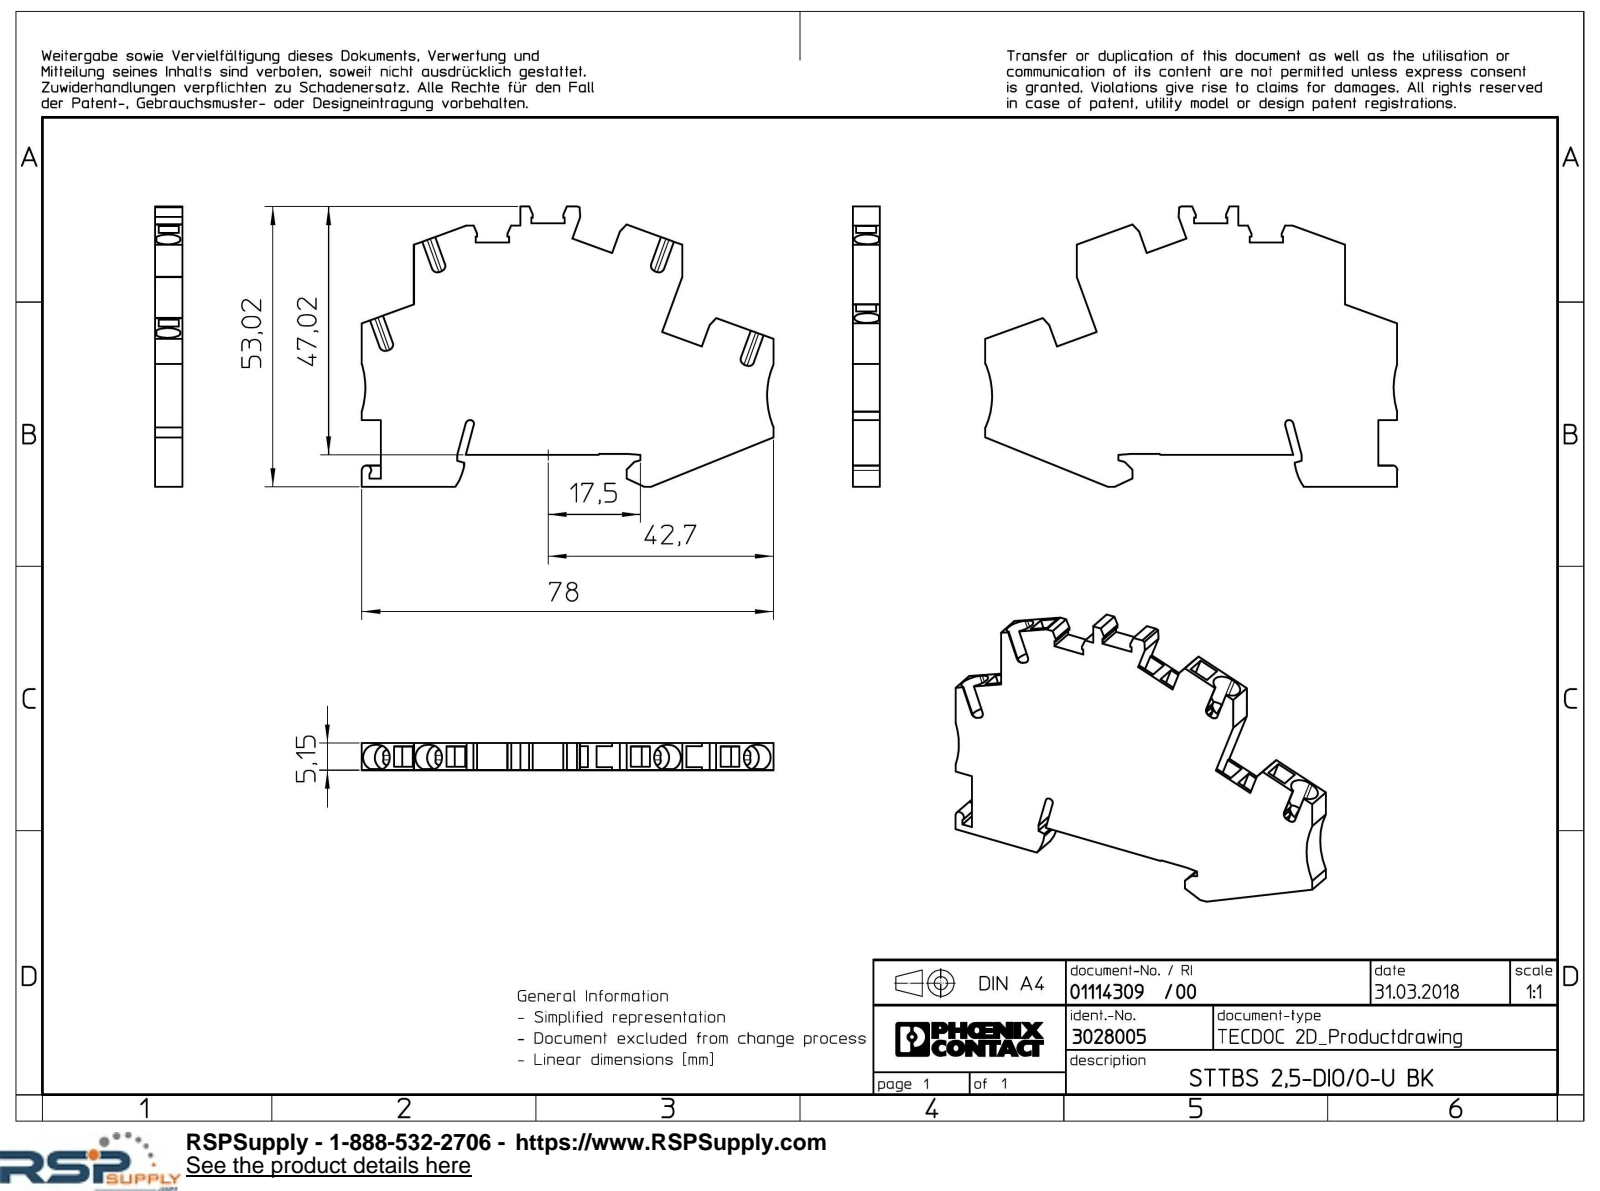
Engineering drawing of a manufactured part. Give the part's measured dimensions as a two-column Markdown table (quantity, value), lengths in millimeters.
| quantity | value |
| --- | --- |
| part name | STTBS2.5-DIO-O-U-BK-Select |
| STEP written by | Creo Elements/Direct Modeling 18.1I 14-Aug-2016 (C) Parametric Technology GmbH (AUTOMOTIVE_DESIGN) |
| units | millimeters |
| bodies | 1 solid, 199 faces (156 planar, 31 cylindrical, 12 other) |
| overall size | 78 × 53.02 × 5.15 |
| volume | 13 020 mm³ |
| surface area | 9 168 mm² |
| partial cylindrical surfaces (radius × count) | 1 × 16, 2.4 × 8, 15 × 2, 0.2 × 1, 0.7 × 1, 0.8 × 1, 0.9 × 1, 9.5 × 1 |
| main face-to-face distances | 5.15, 3.15, 22.03, 3.8, 4, 0.65, 4.57, 0.58, 0.57, 4.58 |
